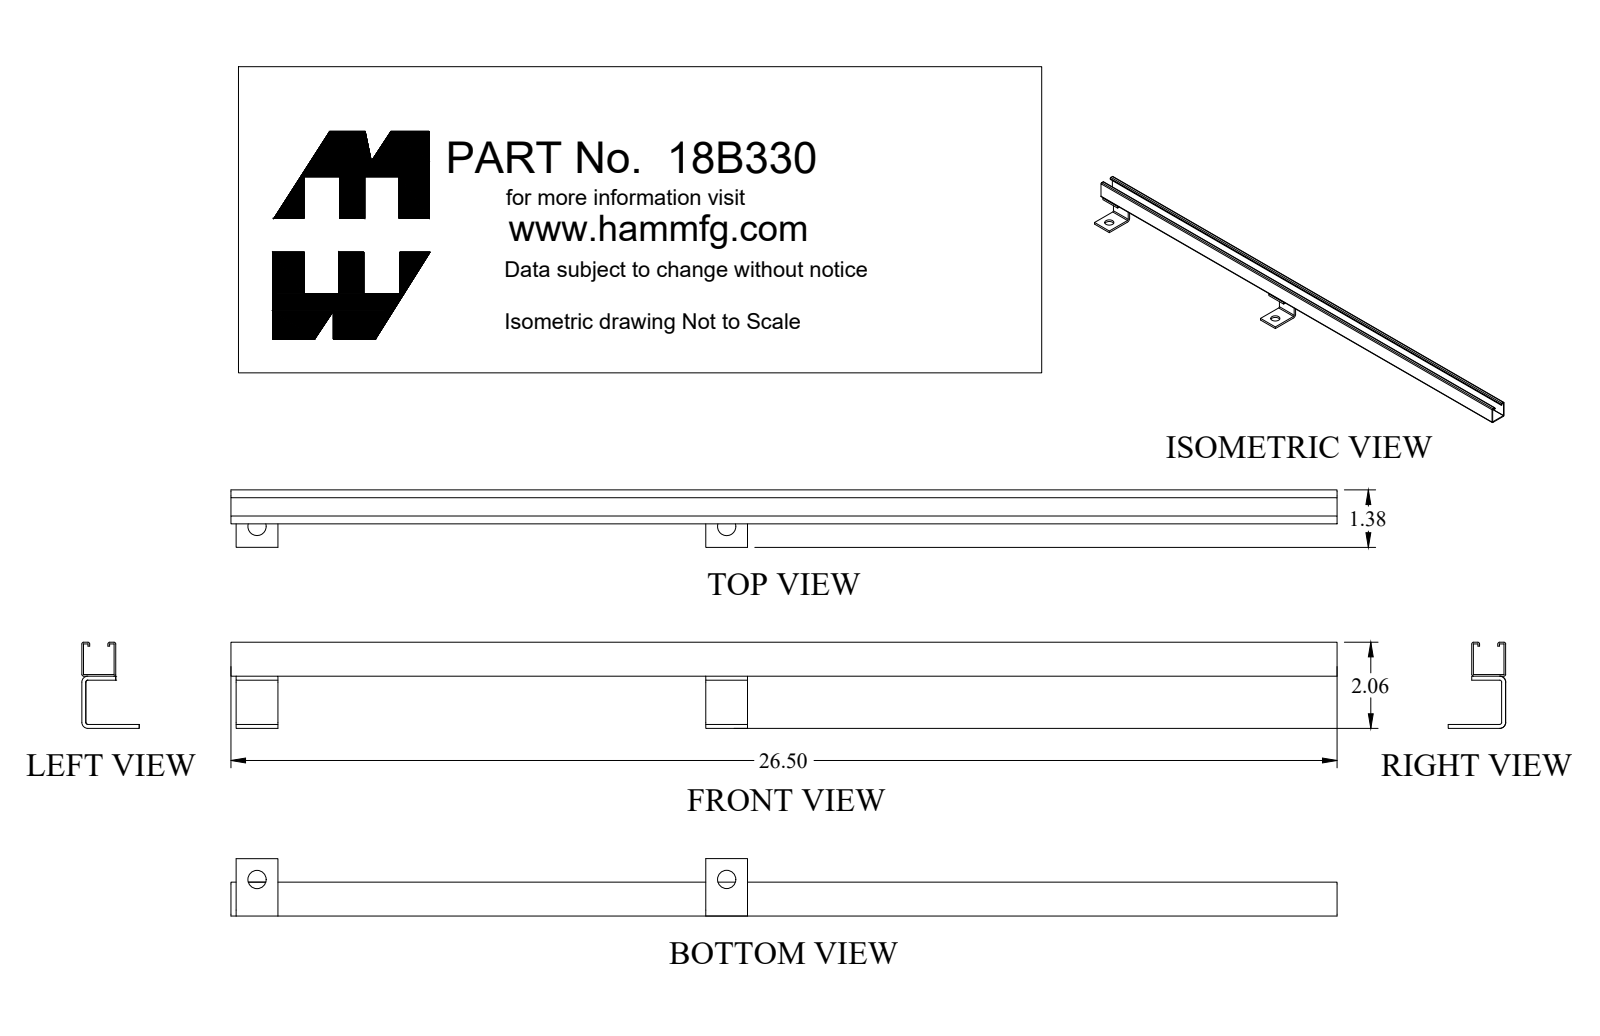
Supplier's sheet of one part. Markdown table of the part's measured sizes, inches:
| quantity | value |
| --- | --- |
| part name | 18B330 |
| STEP written by | SolidWorks 2018 (AUTOMOTIVE_DESIGN) |
| units | inches |
| bodies | 3 solids, 60 faces (38 planar, 22 cylindrical, 0 other) |
| overall size | 26.5 × 2.063 × 1.376 |
| volume | 3.439 in³ |
| surface area | 159.5 in² |
| round holes (diameter × count) | 0.437 × 2 |
| partial cylindrical surfaces (radius × count) | 0.043 × 6, 0.048 × 4, 0.143 × 4 |
| main face-to-face distances | 0.04, 0.773, 0.813, 0.733, 0.773, 0.813, 0.733, 0.625, 0.148, 0.095 |
| hole center spacings | 11.25 |
